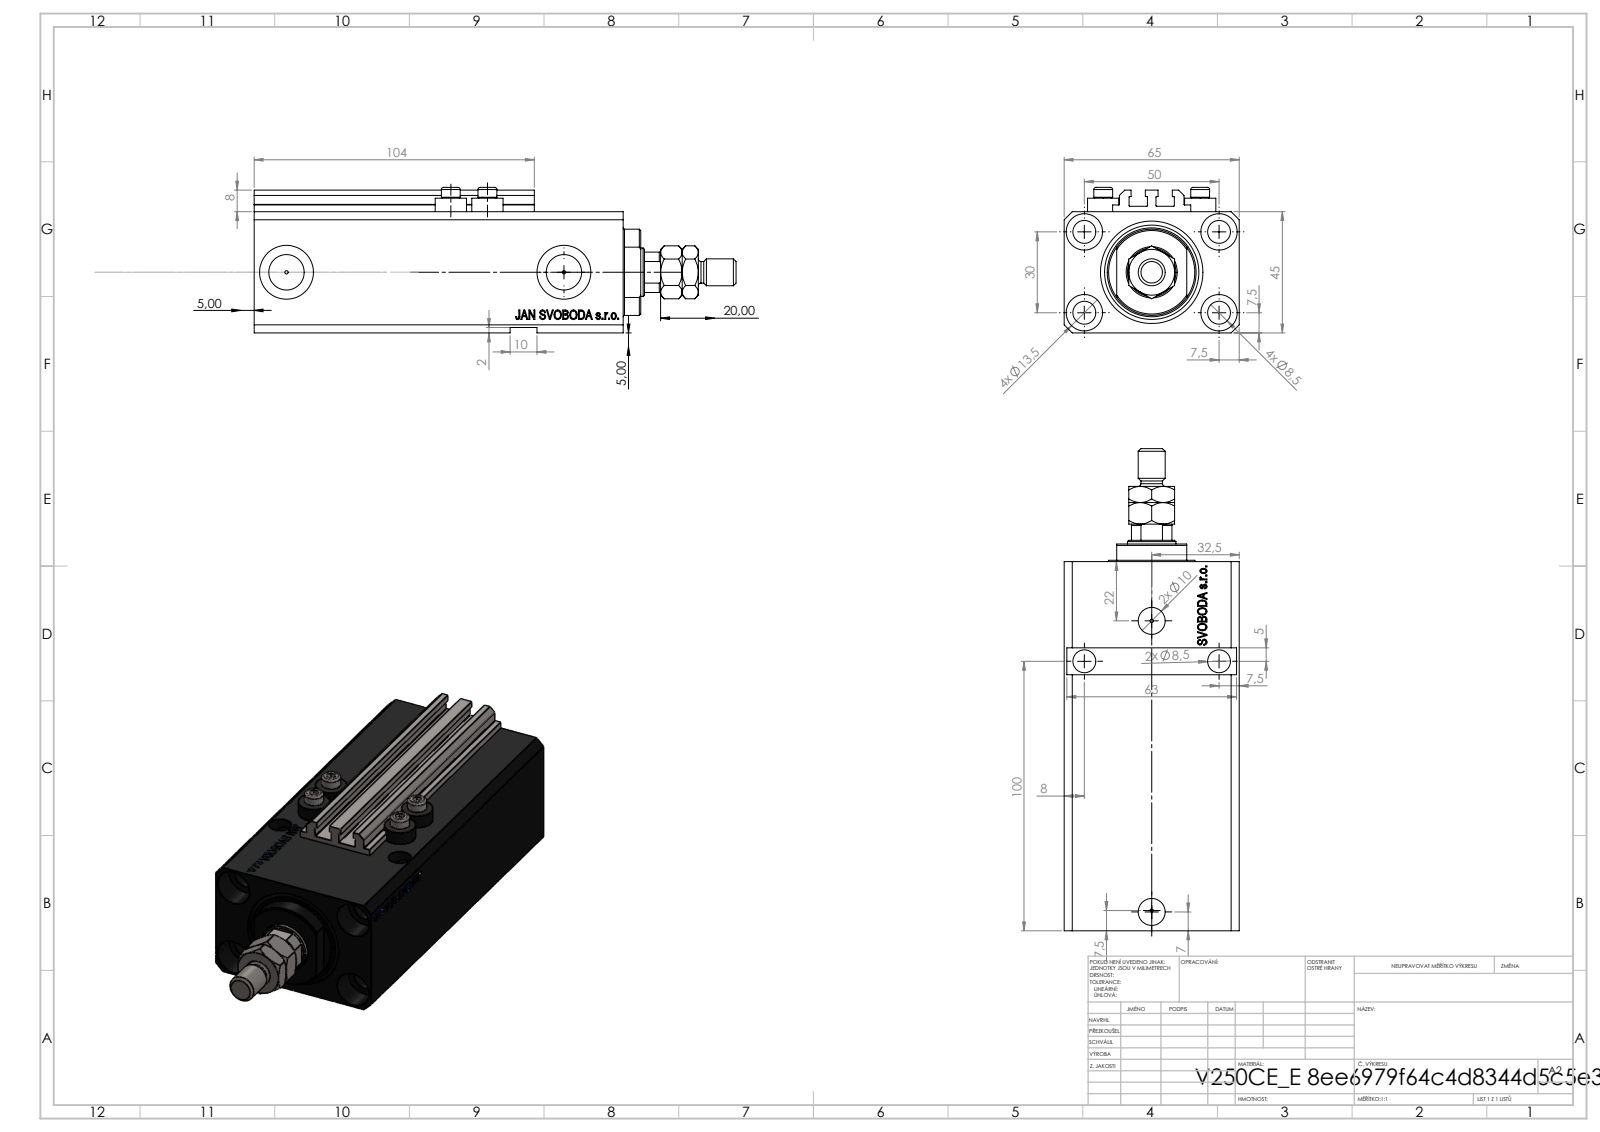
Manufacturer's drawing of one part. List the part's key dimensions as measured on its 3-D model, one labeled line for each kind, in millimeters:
Part name (STEP PRODUCT): V250CE_E_Body; MTA; ALLEN BOLT V250CE; V250CE_C_VCP (+1 more)
STEP written by: SolidWorks 2019 (CONFIG_CONTROL_DESIGN)
Units: millimetres
Bodies: 9 solids, 1136 faces (526 planar, 150 cylindrical, 460 other)
Overall size (bounding box): 179 × 65 × 54
Volume: 354 980 mm³ · Surface area: 95 284 mm²
Round holes (diameter × count): ⌀8.5 ×9, ⌀1.25 ×4, ⌀4 ×4, ⌀13.5 ×4, ⌀10 ×2, ⌀13.16 ×2, ⌀20 ×2, ⌀18 ×1, ⌀25 ×1, ⌀38 ×1
Round bosses / shafts (diameter × count): ⌀11.6 ×4, ⌀7 ×4, ⌀10 ×1, ⌀8 ×1
Partial cylindrical surfaces — rounded edges, fillets, slot ends (radius × count): R0.2 ×10, R8.5 ×1, R16 ×1
Main face-to-face distances: 45, 65, 47, 14, 2, 123, 2.5, 10, 20.5, 6
Hole centre spacings: 29.15, 50, 13.6, 15.12, 27.89, 30, 33.61, 33.62
